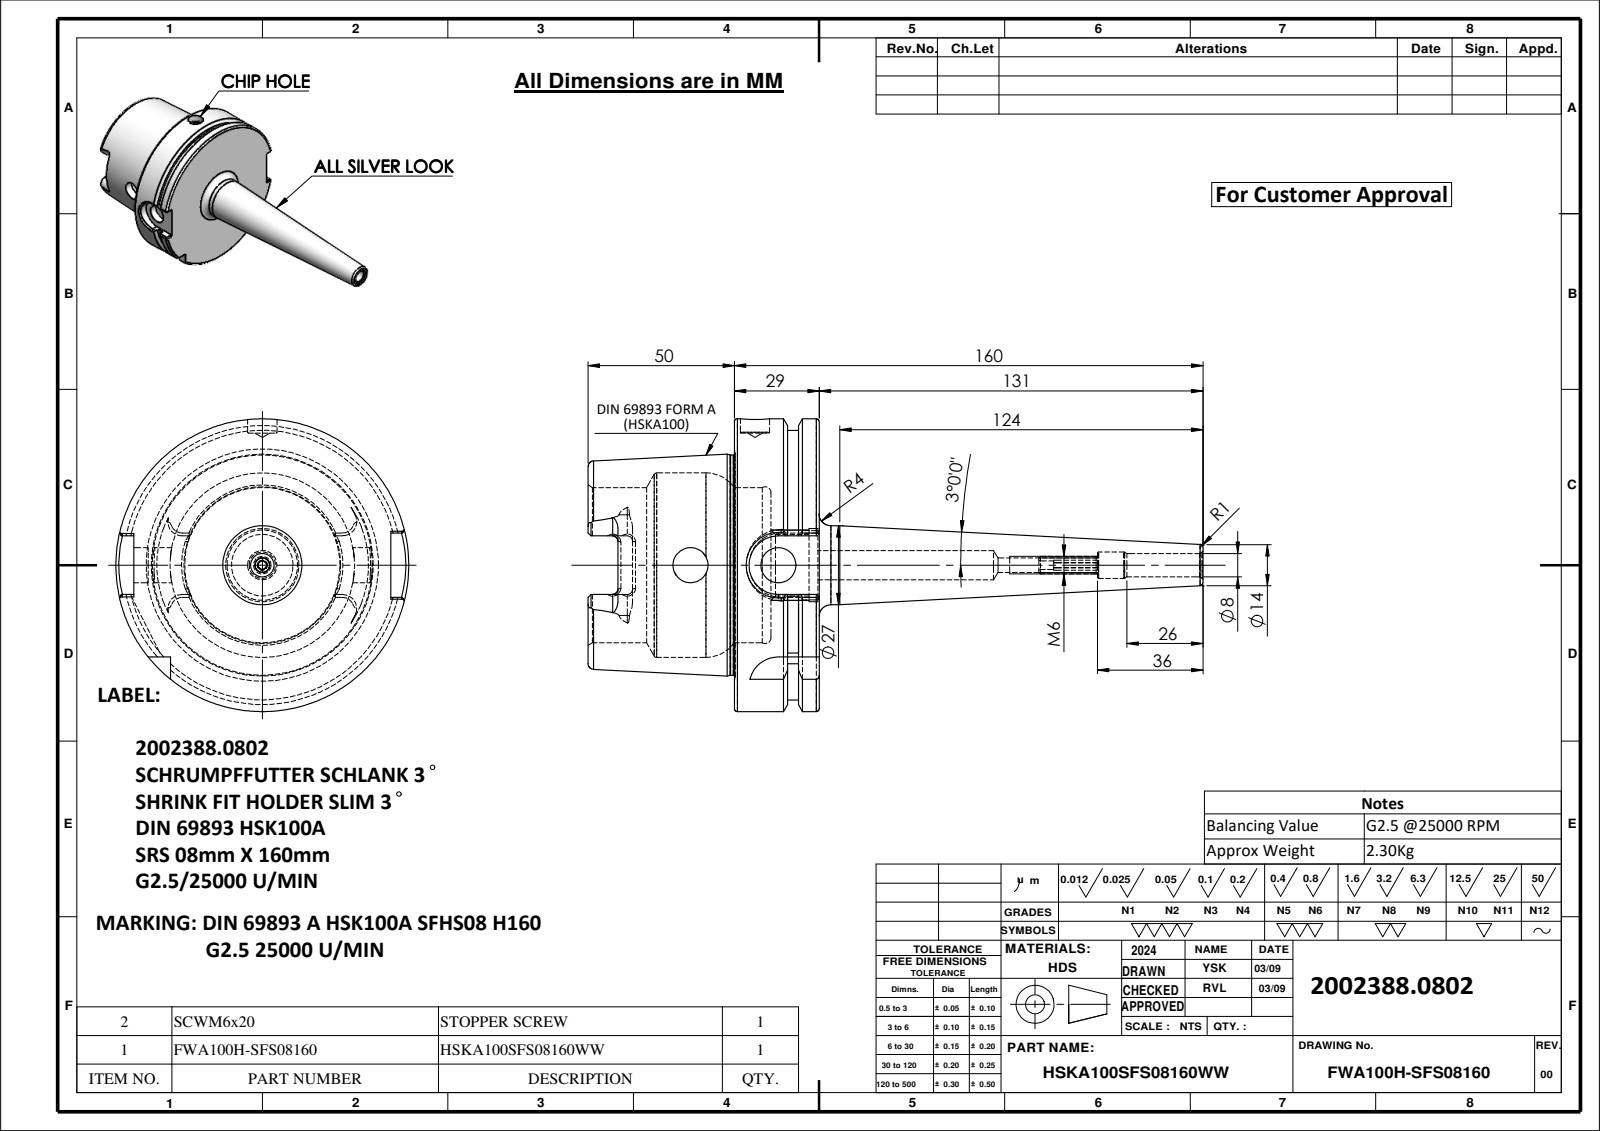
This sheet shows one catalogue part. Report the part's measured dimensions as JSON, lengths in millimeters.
{"part_name": "FWA100H-SFS08160; HSKA100SFS08160WW; SCWM6", "step_written_by": "SolidWorks 2024 (CONFIG_CONTROL_DESIGN)", "units": "millimeters", "bodies": {"solids": 2, "faces": 205, "planar": 61, "cylindrical": 58, "other": 86}, "overall_size": [210, 100, 100], "volume_mm3": 293307, "surface_area_mm2": 61847, "round_holes": [[10, 2], [12, 2], [2.9, 1], [5, 1], [8, 1], [9, 1], [21, 1], [25, 1], [53, 1], [63, 1]], "round_bosses_or_shafts": [[100, 1], [92, 1], [75.16, 1], [27, 1], [6, 1]], "partial_cylinders_radius": [[1.8, 6], [4.88, 4], [10, 2], [11, 1]], "face_to_face_distances": [28.95, 12.5, 16.45, 50, 62.5, 78.95, 78.5, 28.5, 16, 0.45], "hole_center_spacings": [30]}
